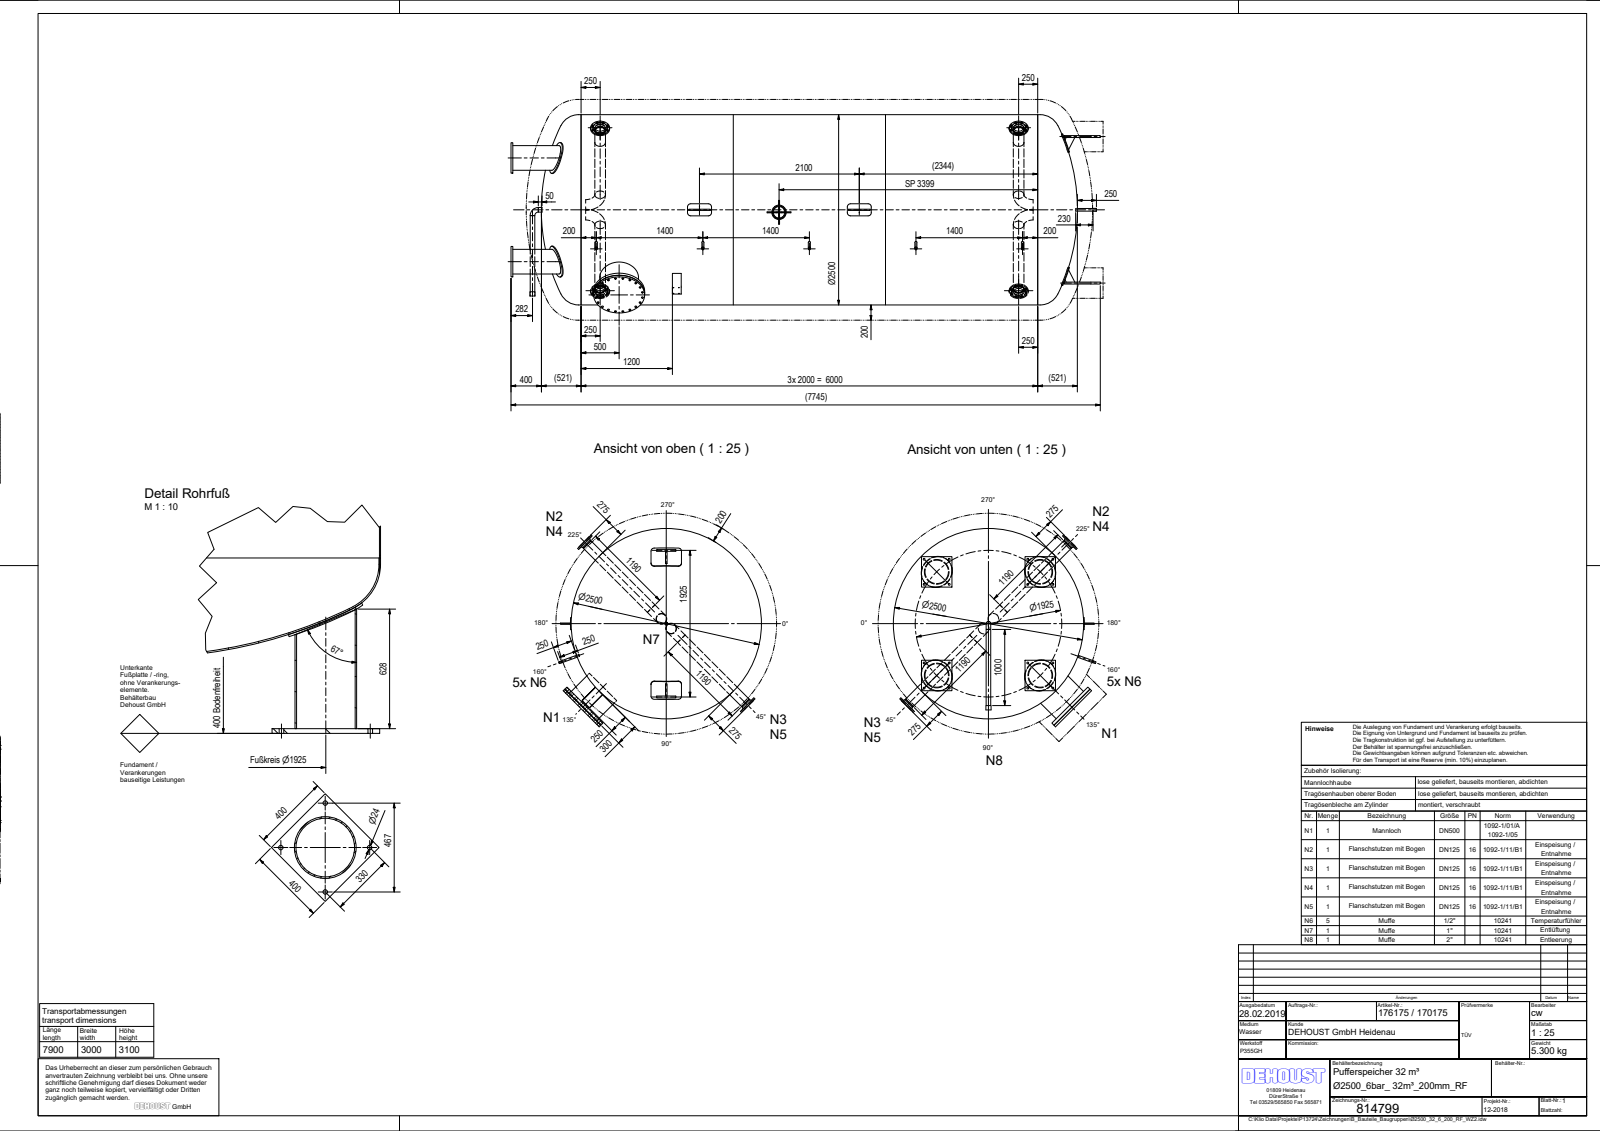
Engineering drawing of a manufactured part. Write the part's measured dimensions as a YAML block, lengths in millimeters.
part_name: "Ø2500_32_6_200_RF_WZ2; Klöpper_Gew_Ø2500_8,3; Zyl_Ø2500_6x6000_2019; TÖB_Puffer_Ø2500_8, 3_200 (+8 more)"
step_written_by: "Autodesk Inventor 2019 (AUTOMOTIVE_DESIGN)"
units: millimeters
bodies: {solids: 58, faces: 453, planar: 178, cylindrical: 225, other: 50}
overall_size: [7745.05, 2664.05, 2604.82]
volume: 607200000
surface_area: 138400000
round_holes:
  - {diameter: 26, count: 40}
  - {diameter: 18, count: 32}
  - {diameter: 24, count: 16}
  - {diameter: 131.7, count: 8}
  - {diameter: 18.63, count: 5}
  - {diameter: 21.7, count: 5}
  - {diameter: 26.9, count: 5}
  - {diameter: 5.8, count: 4}
  - {diameter: 139.7, count: 4}
  - {diameter: 307.9, count: 4}
  - {diameter: 5, count: 2}
  - {diameter: 52.3, count: 2}
round_bosses_or_shafts:
  - {diameter: 139.7, count: 8}
  - {diameter: 26.9, count: 5}
  - {diameter: 26.4, count: 5}
  - {diameter: 420, count: 4}
  - {diameter: 323.9, count: 4}
  - {diameter: 250, count: 4}
  - {diameter: 188, count: 4}
  - {diameter: 670, count: 2}
partial_cylinders:
  - {radius: 42, count: 16}
  - {radius: 6, count: 8}
  - {radius: 5, count: 2}
  - {radius: 10, count: 2}
  - {radius: 36, count: 2}
  - {radius: 72, count: 2}
  - {radius: 125, count: 1}
  - {radius: 1259, count: 1}
face_to_face_distances: [25, 600, 3733.97, 4108.97, 3708.97, 4083.97, 375, 27.99, 2812.5, 3187.5]
hole_center_spacings: [310, 105, 191.59, 1400, 5500, 501.59, 194.02, 2800]
